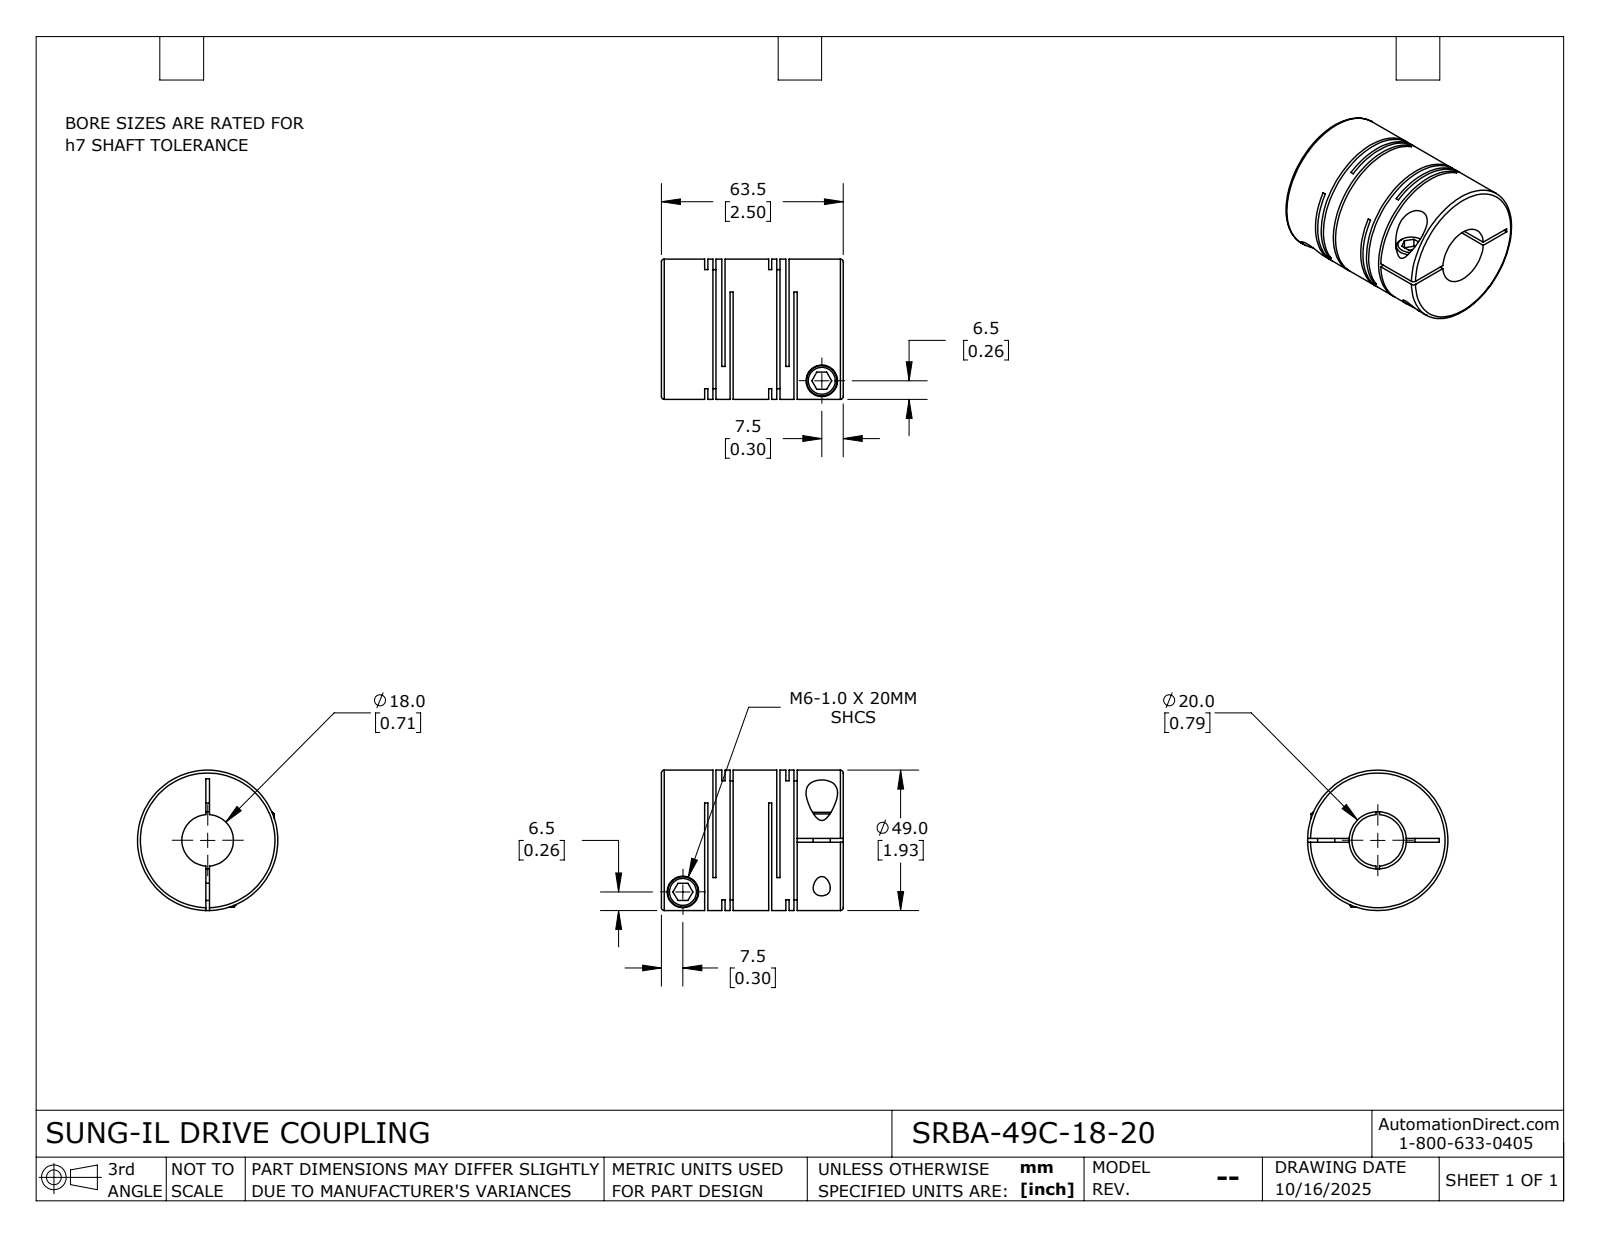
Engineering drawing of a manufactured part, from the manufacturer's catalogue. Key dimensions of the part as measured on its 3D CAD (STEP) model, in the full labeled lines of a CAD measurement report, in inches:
Part name (STEP PRODUCT): SRBA-49C-18-20
STEP written by: SolidWorks 2024 (CONFIG_CONTROL_DESIGN)
Units: inches
Bodies: 1 solid, 115 faces (60 planar, 42 cylindrical, 13 other)
Overall size (bounding box): 2.5 × 1.929 × 1.929
Volume: 5.313 in³ · Surface area: 58.99 in²
Round holes (diameter × count): ⌀0.236 ×2, ⌀0.433 ×2, ⌀0.709 ×1, ⌀0.787 ×1
Round bosses / shafts (diameter × count): ⌀0.417 ×2, ⌀1.929 ×1
Main face-to-face distances: 0.236, 0.043, 0.88, 0.112, 0.837, 0.124, 0.069, 0.193, 0.768, 0.644
